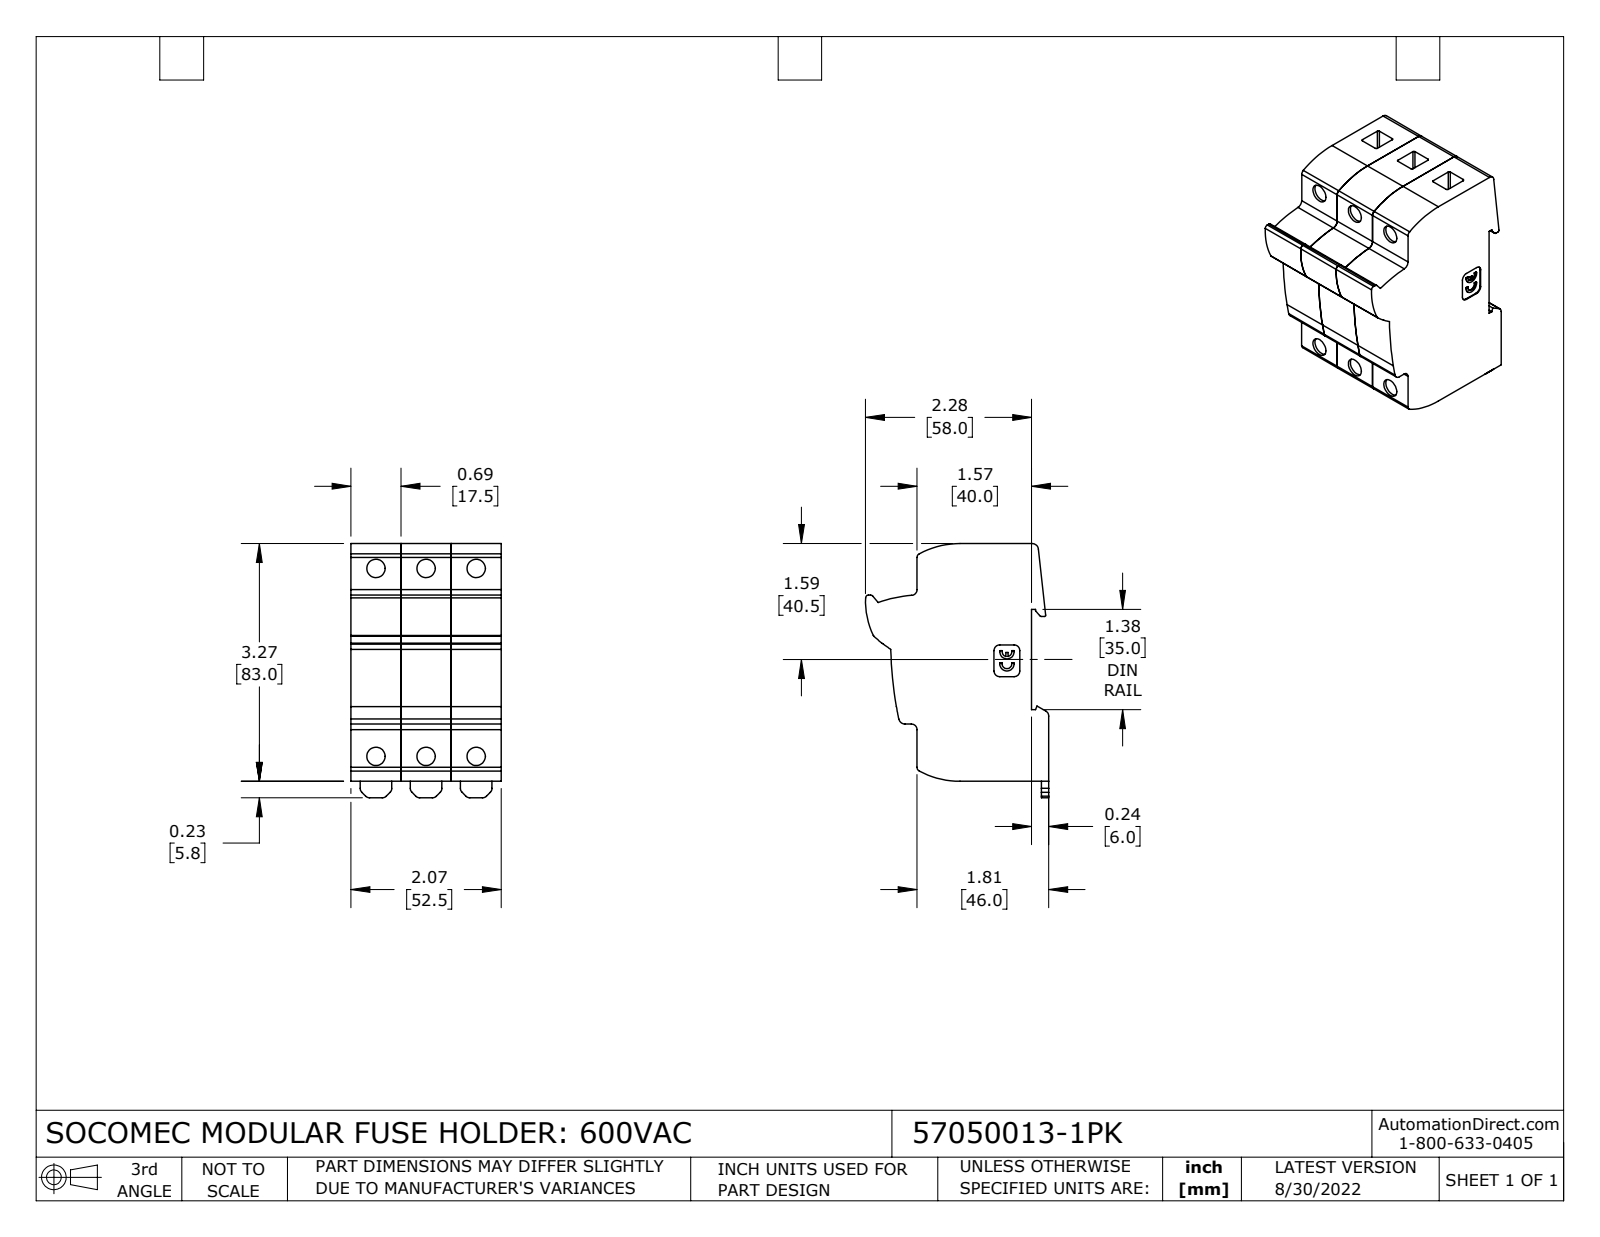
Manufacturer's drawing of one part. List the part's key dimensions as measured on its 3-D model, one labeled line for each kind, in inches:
Part name (STEP PRODUCT): 57050013-1PK
STEP written by: SolidWorks 2021 (CONFIG_CONTROL_DESIGN)
Units: inches
Bodies: 3 solids, 315 faces (156 planar, 159 cylindrical, 0 other)
Overall size (bounding box): 3.496 × 2.52 × 2.067
Volume: 12.69 in³ · Surface area: 64 in²
Round holes (diameter × count): ⌀0.252 ×6
Partial cylindrical surfaces — rounded edges, fillets, slot ends (radius × count): R0.079 ×19, R0.02 ×13, R0.039 ×4, R0.059 ×2, R0.067 ×2, R0.087 ×2, R0.098 ×2, R1.186 ×2
Main face-to-face distances: 0.689, 1.378, 2.067, 0.236, 1.575, 3.268, 1.811, 0.199, 0.49, 0.888
Hole centre spacings: 0.689, 2.673, 2.583, 1.378, 2.927
